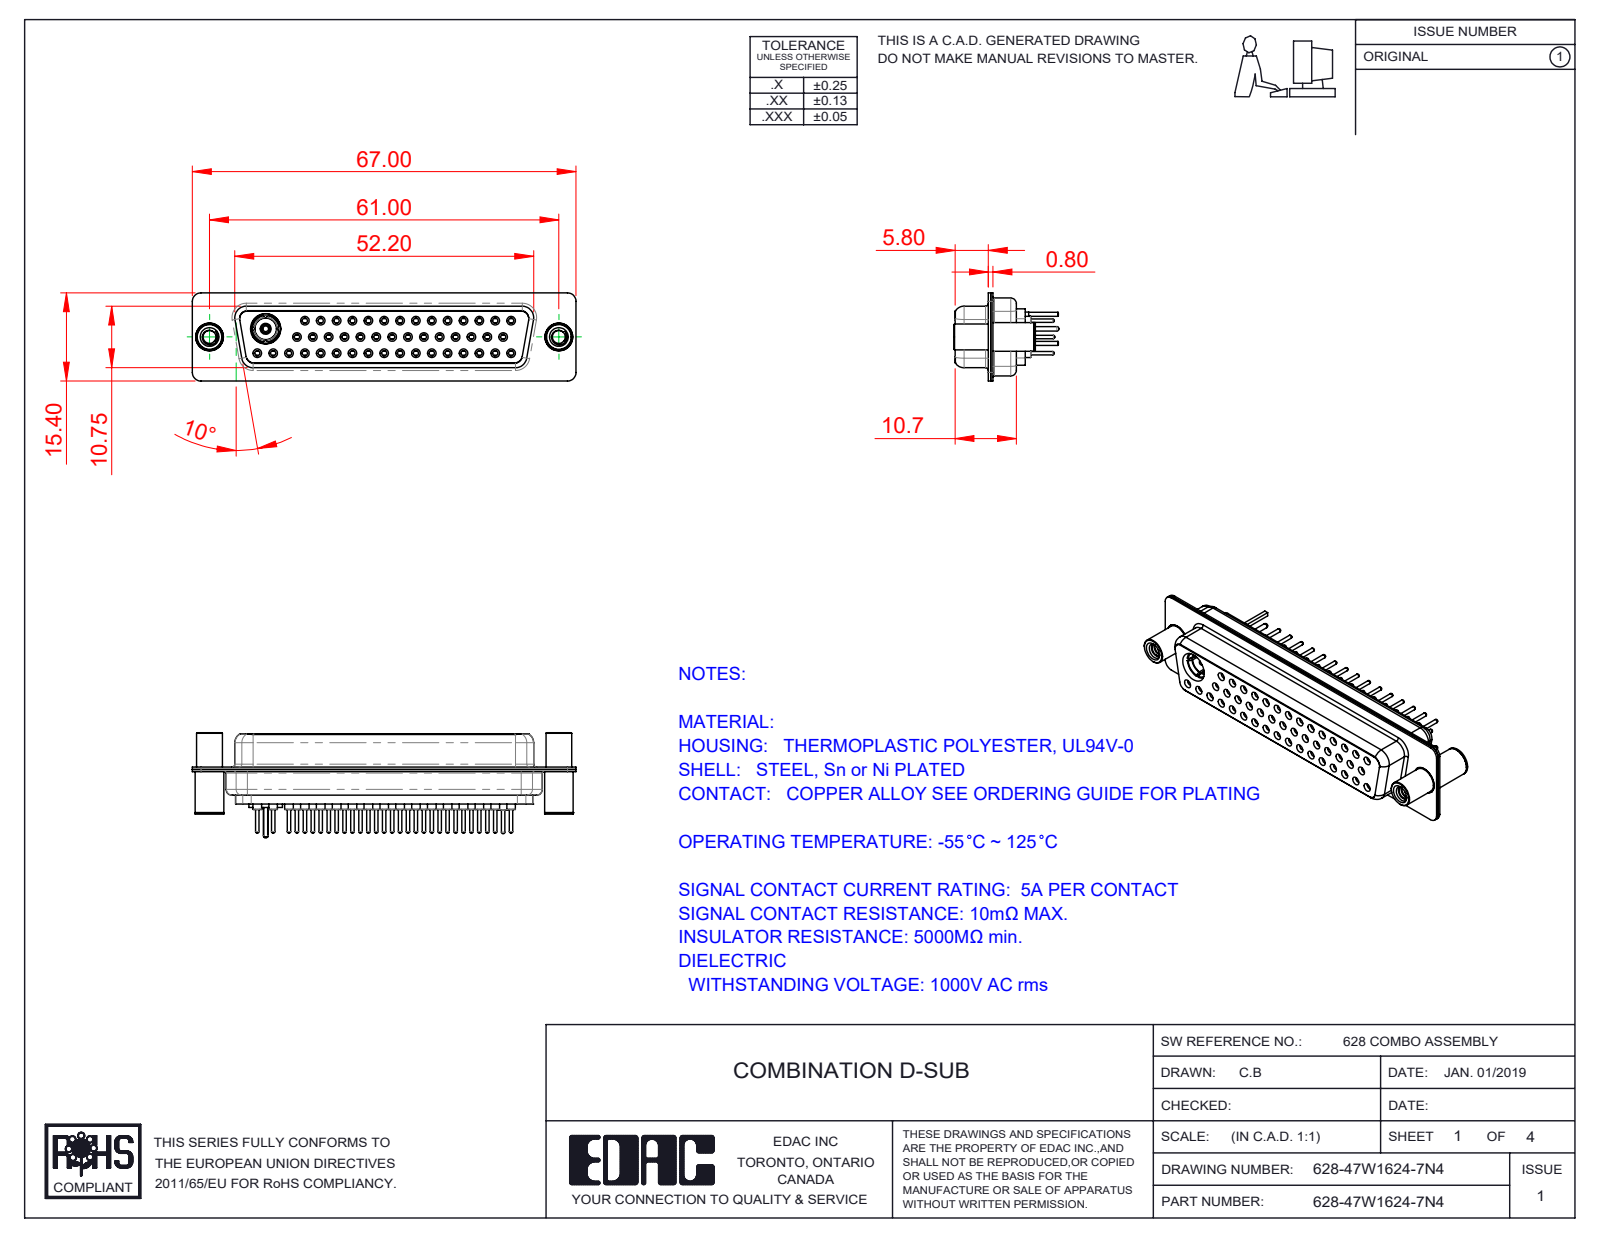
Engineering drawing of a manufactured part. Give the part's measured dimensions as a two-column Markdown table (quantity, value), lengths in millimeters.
| quantity | value |
| --- | --- |
| part name | Locking Collar; 628Combo Housing_47W1; 628Combo Shell Front_50 Contacts; 628Combo Contact Row 1_24 (+8 more) |
| STEP written by | SolidWorks 2016 (CONFIG_CONTROL_DESIGN) |
| units | millimeters |
| bodies | 55 solids, 3009 faces (817 planar, 1100 cylindrical, 1092 other) |
| overall size | 67 × 18.35 × 15.4 |
| volume | 7 332 mm³ |
| surface area | 15 409 mm² |
| round holes (diameter × count) | 1.1 × 47, 1.5 × 46, 0.9 × 45, 2 × 45, 1.6 × 31, 1.7 × 14, 4.85 × 3, 2.26 × 2, 3.26 × 2, 4 × 2, 4.05 × 2, 2.83 × 1 |
| round bosses / shafts (diameter × count) | 2.2 × 46, 0.6 × 46, 1.6 × 15, 5 × 3, 4.95 × 2, 4.8 × 2, 4.5 × 2, 5.85 × 1 |
| partial cylindrical surfaces (radius × count) | 1.5 × 16, 1.35 × 12, 2 × 12, 1.6 × 8, 0.25 × 4, 0.5 × 4, 0.6 × 4, 0.65 × 4 |
| main face-to-face distances | 0.4, 6.05, 11.33, 6.45, 1.87, 12.25, 6.2, 5.8, 10.35, 10.93 |
| hole center spacings | 3.16, 2.77, 5.54, 8.31, 11.08, 13.85, 16.62, 19.39 |
